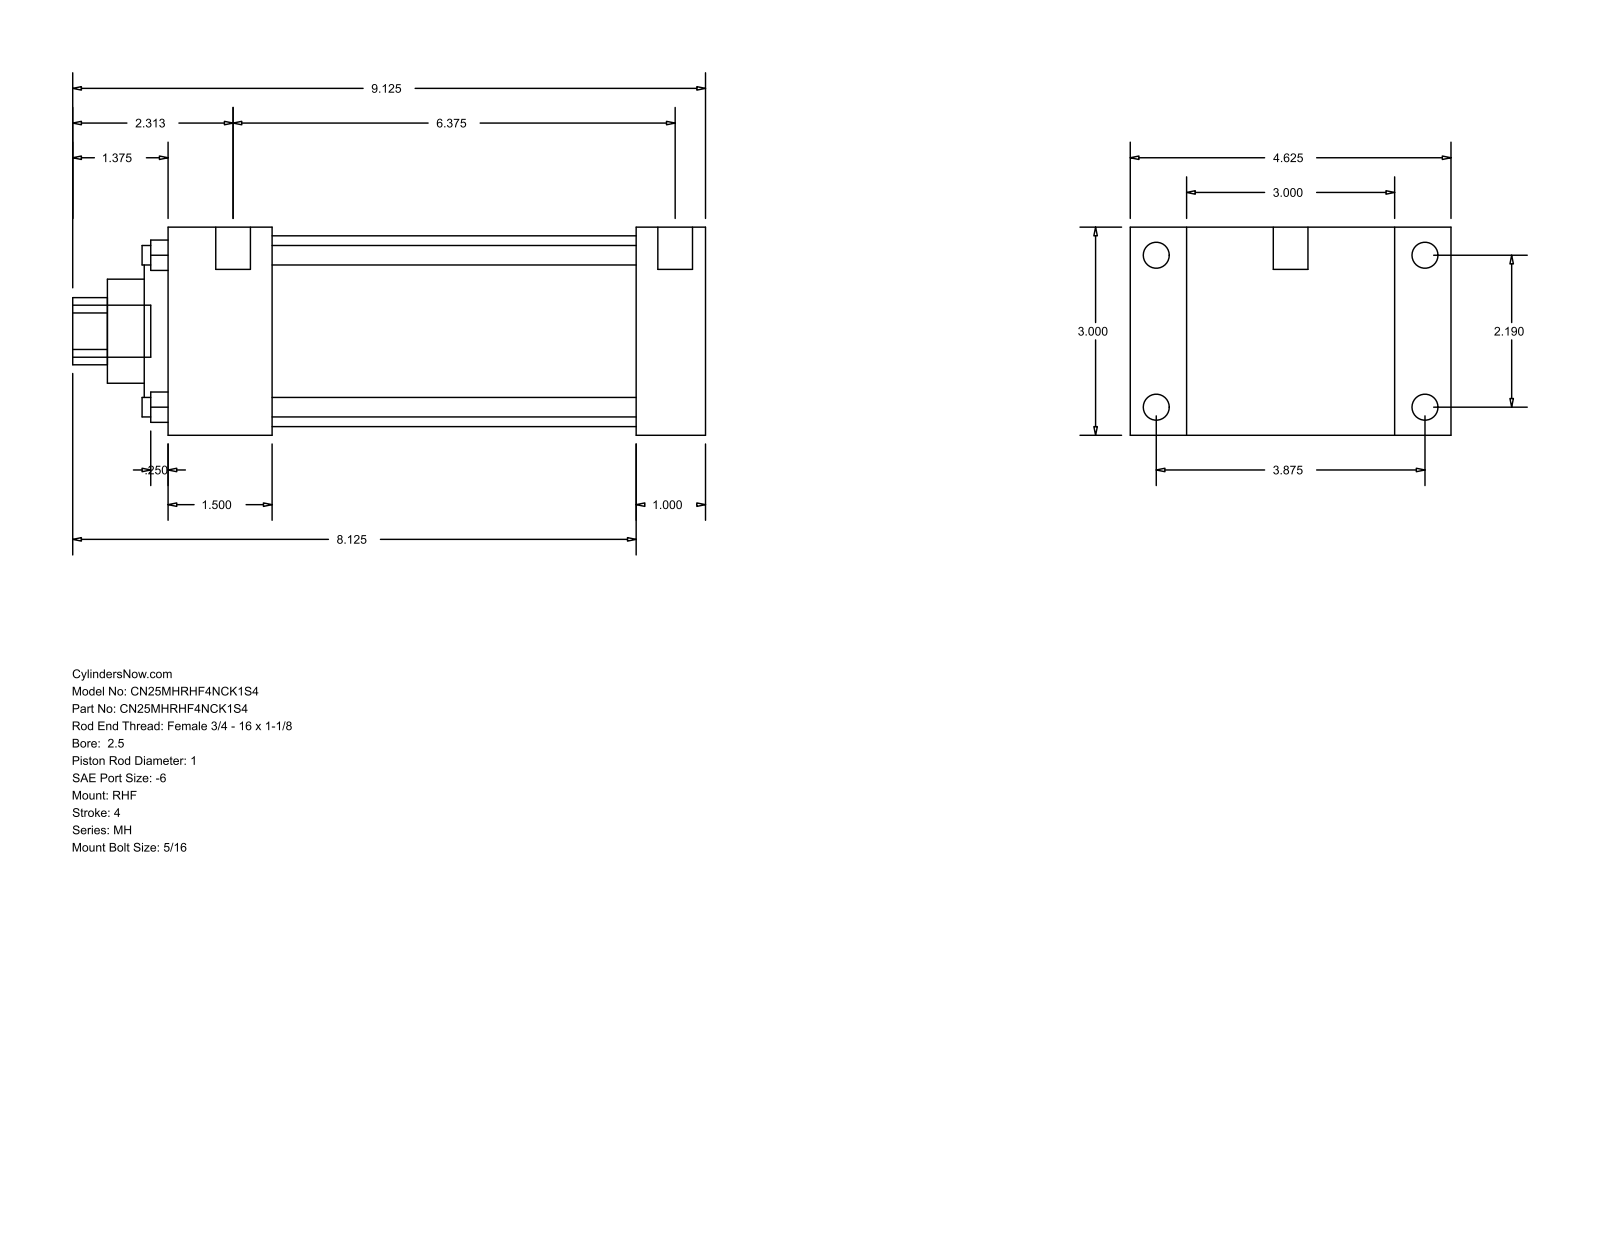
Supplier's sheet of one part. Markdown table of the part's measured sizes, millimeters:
| quantity | value |
| --- | --- |
| part name | MH_RHF__0250_1 |
| STEP written by | GSSL Pune (CONFIG_CONTROL_DESIGN) |
| units | millimeters |
| bodies | 0 solids, 90 faces (61 planar, 29 cylindrical, 0 other) |
| overall size | 231.78 × 117.47 × 76.2 |
| round holes (diameter × count) | 7.14 × 4, 25.4 × 1, 38.1 × 1, 60.33 × 1, 69.85 × 1 |
| round bosses / shafts (diameter × count) | 9.53 × 4, 5.56 × 4, 12.7 × 2, 19.05 × 1 |
| partial cylindrical surfaces (radius × count) | 12.29 × 1 |
| main face-to-face distances | 76.2, 25.4, 20.64, 96.84, 171.46, 196.86, 117.48, 38.11, 133.35, 158.75 |
| hole center spacings | 39.33, 55.62, 78.66 |
